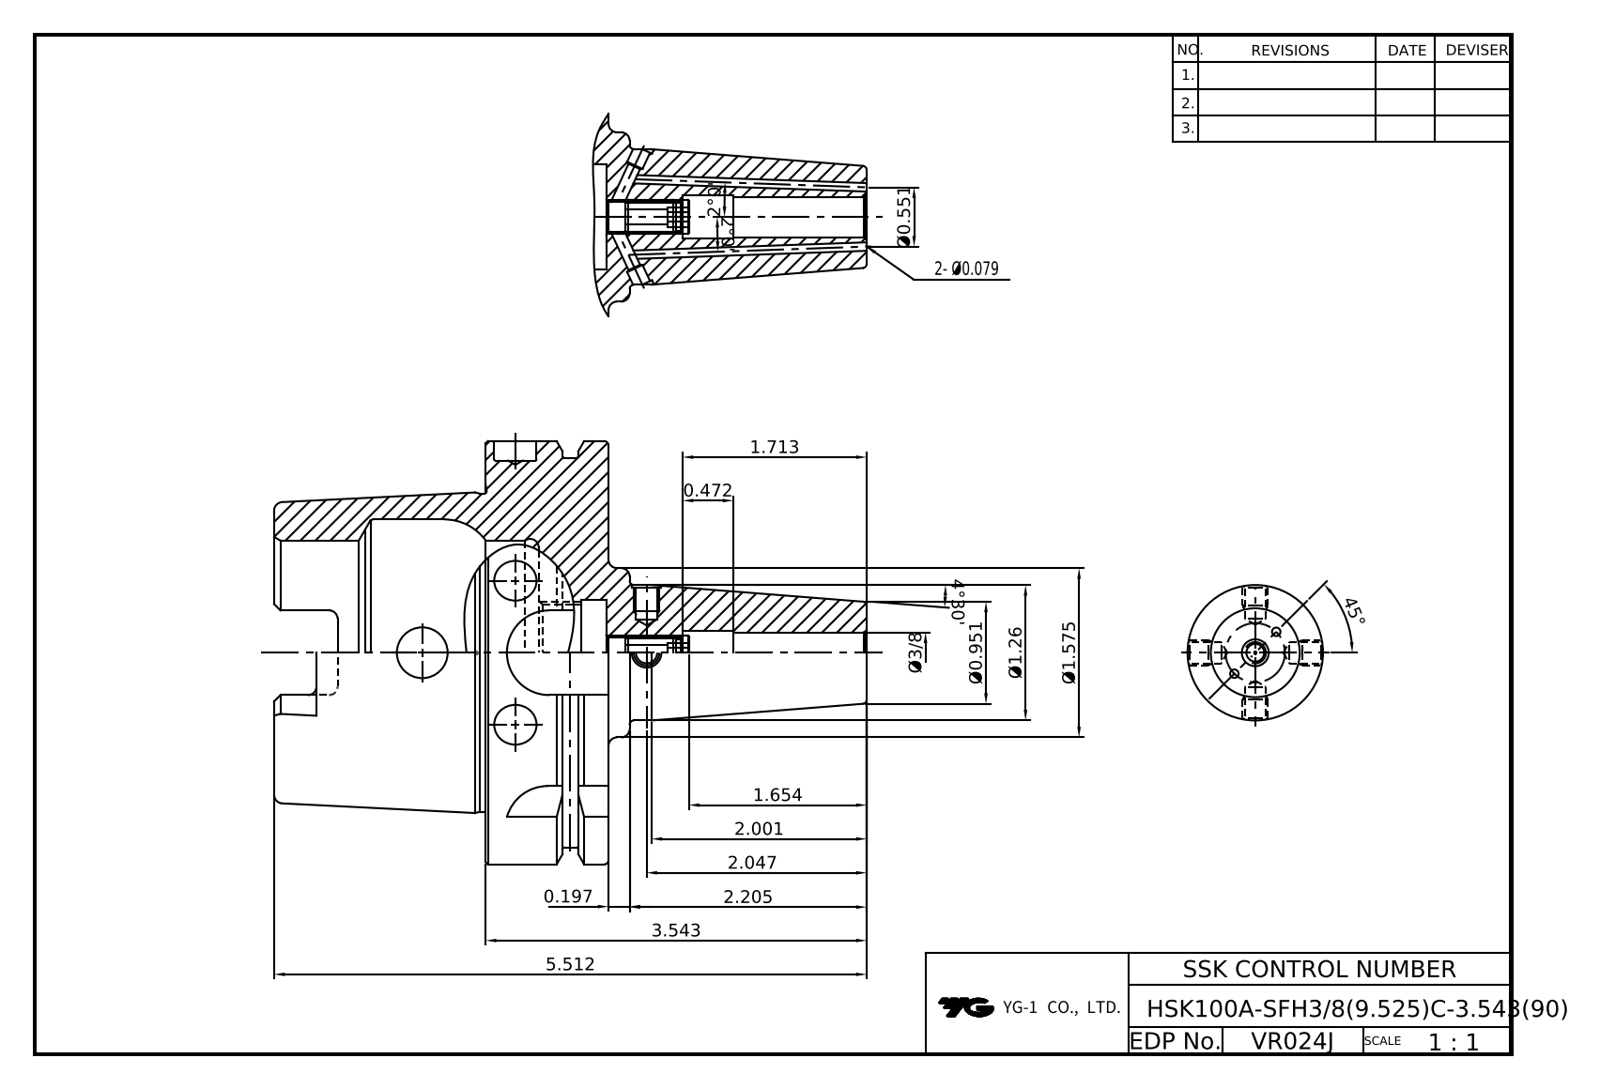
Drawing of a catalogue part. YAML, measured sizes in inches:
part_name: "LO-HSK100A-SFH9.525C-90"
step_written_by: "Autodesk Inventor 2022 (AUTOMOTIVE_DESIGN)"
units: inches
bodies: {solids: 1, faces: 121, planar: 39, cylindrical: 37, other: 45}
overall_size: [5.512, 3.937, 3.937]
volume: 17.81
surface_area: 88.5
round_holes:
  - {diameter: 0.079, count: 2}
  - {diameter: 0.272, count: 1}
  - {diameter: 0.375, count: 1}
  - {diameter: 0.394, count: 1}
  - {diameter: 0.422, count: 1}
  - {diameter: 0.472, count: 1}
  - {diameter: 0.881, count: 1}
  - {diameter: 0.984, count: 1}
  - {diameter: 2.087, count: 1}
  - {diameter: 2.48, count: 1}
round_bosses_or_shafts:
  - {diameter: 3.937, count: 1}
  - {diameter: 3.622, count: 1}
  - {diameter: 2.969, count: 1}
  - {diameter: 1.575, count: 1}
  - {diameter: 1.26, count: 1}
partial_cylinders:
  - {radius: 0.079, count: 6}
  - {radius: 0.192, count: 4}
  - {radius: 0.394, count: 4}
face_to_face_distances: [1.142, 0.492, 0.65, 2.461, 1.969, 3.11, 2.682, 2.83, 3.091, 1.122]
